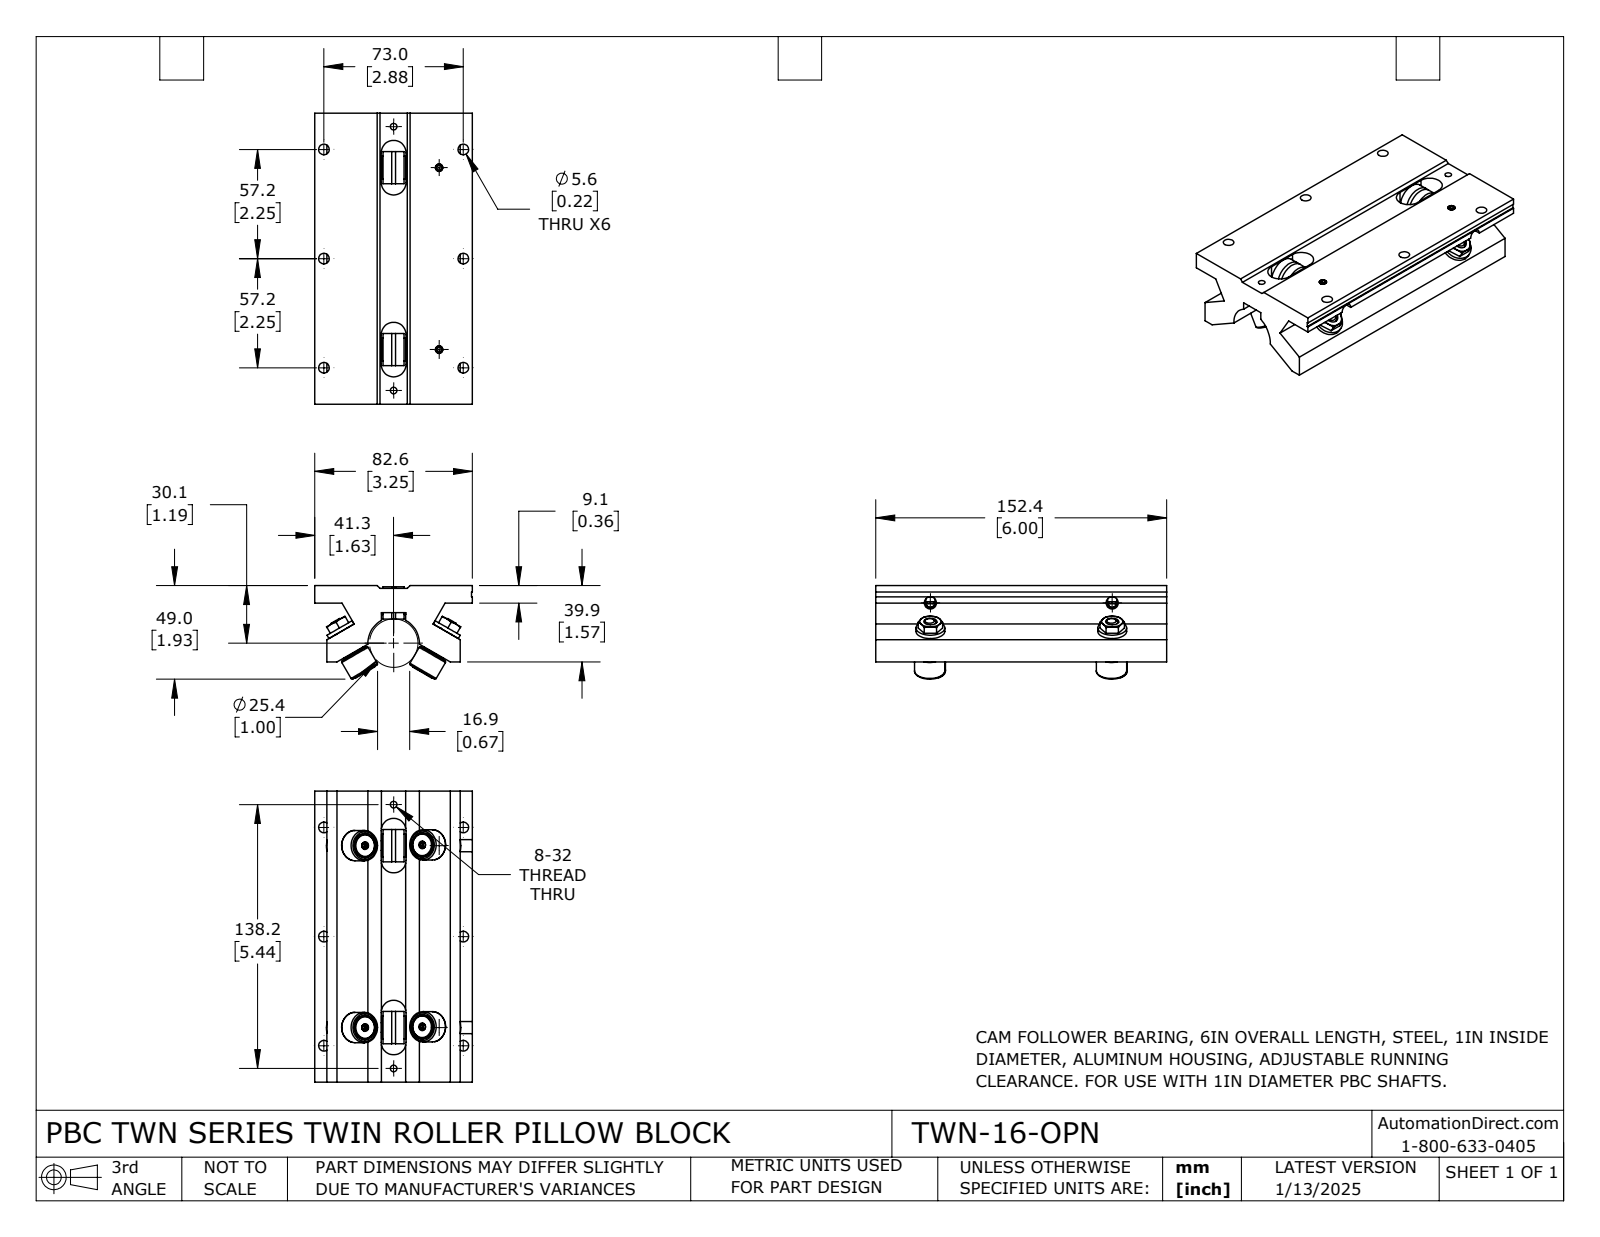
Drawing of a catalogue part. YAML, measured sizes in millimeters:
part_name: "TWN-16-OPN"
step_written_by: "SolidWorks 2023 (CONFIG_CONTROL_DESIGN)"
units: millimeters
bodies: {solids: 16, faces: 529, planar: 216, cylindrical: 165, other: 148}
overall_size: [152.4, 82.6, 49]
volume: 278400
surface_area: 67680
round_holes:
  - {diameter: 5.6, count: 6}
  - {diameter: 3.3, count: 4}
  - {diameter: 5.2, count: 4}
  - {diameter: 12.7, count: 4}
  - {diameter: 3.5, count: 2}
  - {diameter: 3.8, count: 2}
  - {diameter: 4, count: 2}
  - {diameter: 5, count: 2}
  - {diameter: 6.4, count: 2}
  - {diameter: 6.4, count: 2}
  - {diameter: 6.6, count: 2}
  - {diameter: 9.6, count: 2}
round_bosses_or_shafts:
  - {diameter: 15.9, count: 4}
  - {diameter: 15.1, count: 4}
  - {diameter: 11.9, count: 4}
  - {diameter: 16.9, count: 2}
  - {diameter: 12, count: 2}
  - {diameter: 10.3, count: 2}
  - {diameter: 6.6, count: 2}
  - {diameter: 6.5, count: 2}
partial_cylinders:
  - {radius: 6.5, count: 4}
  - {radius: 13.5, count: 1}
face_to_face_distances: [12.7, 9.1, 6.4, 76.2, 152.4, 69.9, 30.8, 39.9, 38.5, 7.7]
hole_center_spacings: [38.4, 57.2, 78.1, 92.7, 95.3, 131.4, 73, 15.8]
